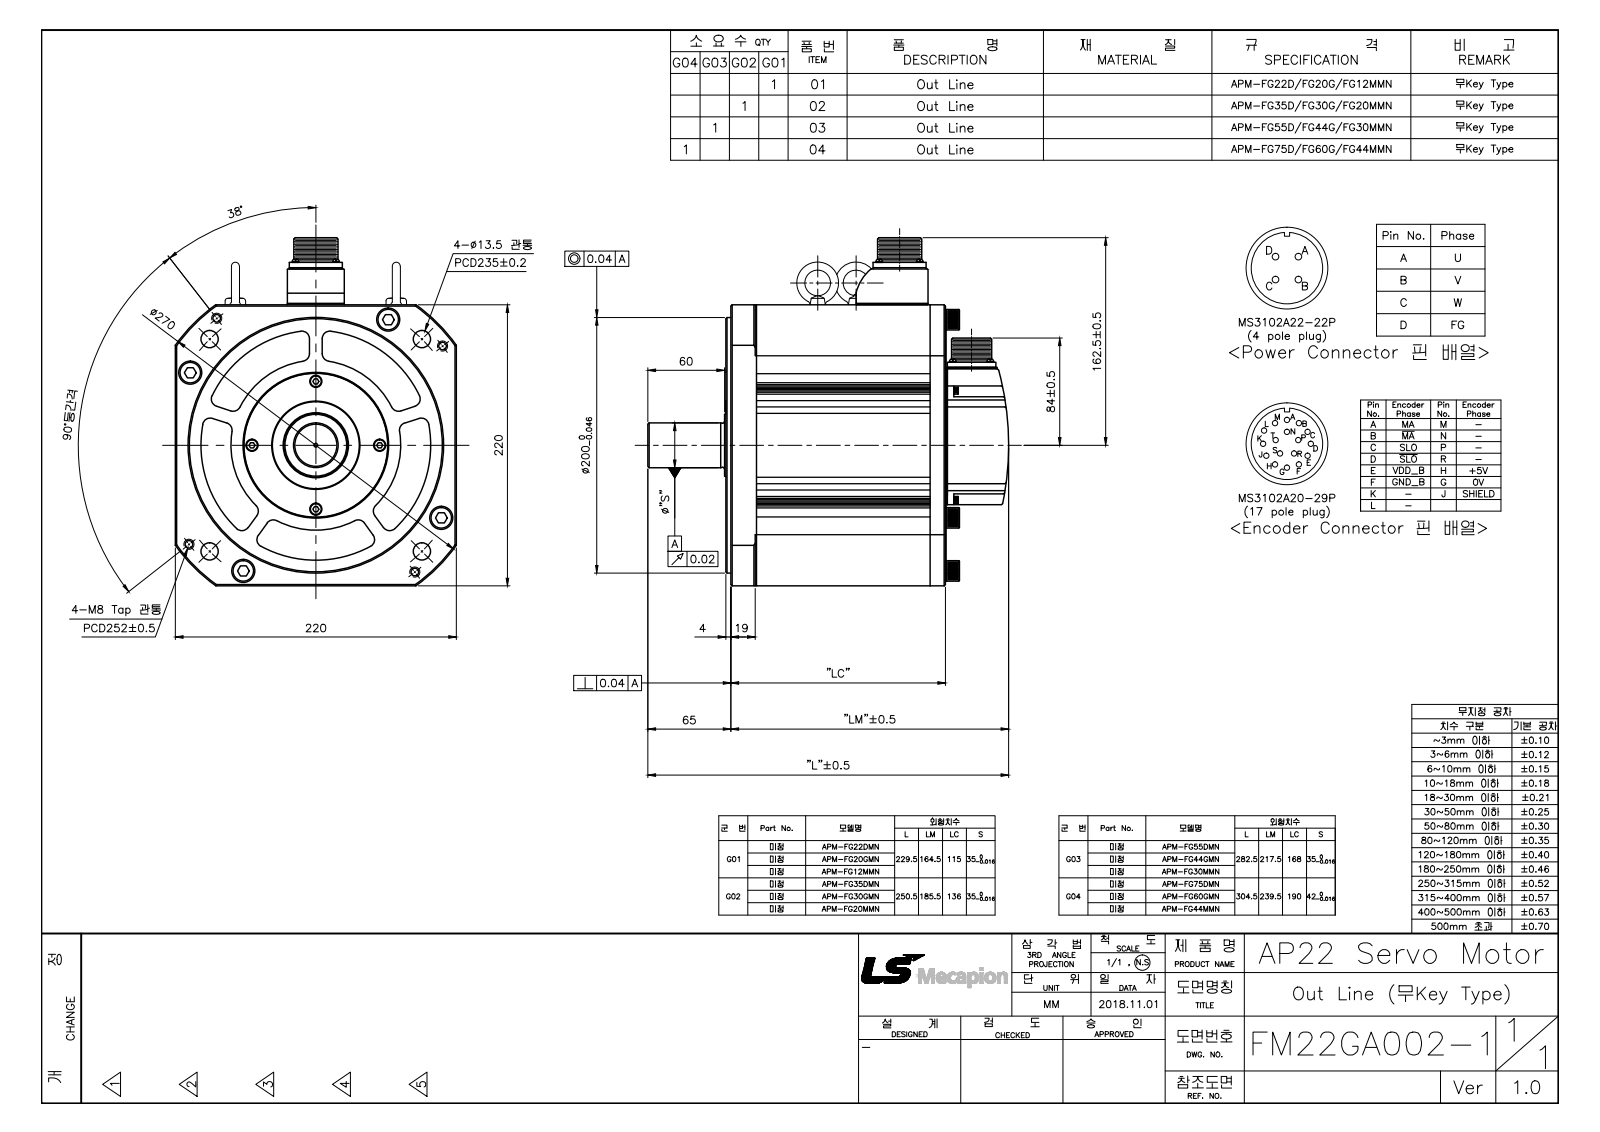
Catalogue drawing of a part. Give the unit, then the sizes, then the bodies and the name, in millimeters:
Units: millimetres
Overall size (bounding box): 282.5 × 272.5 × 220
Round holes (diameter × count): ⌀2.5 ×12, ⌀3 ×12, ⌀3.05 ×8, ⌀6 ×8, ⌀8 ×6, ⌀3.5 ×4, ⌀3.6 ×4, ⌀3.7 ×4, ⌀4.2 ×4, ⌀5 ×4, ⌀8.5 ×4, ⌀9.5 ×4
Round bosses / shafts (diameter × count): ⌀1.6 ×17, ⌀5.4 ×8, ⌀16 ×4, ⌀8.5 ×4, ⌀5.5 ×4, ⌀3 ×4, ⌀201 ×1, ⌀200 ×1
Partial cylindrical surfaces — rounded edges, fillets, slot ends (radius × count): R1 ×112, R6 ×20, R4 ×18, R2 ×17, R5 ×16, R0.5 ×12, R4.5 ×12, R0.3 ×2
Main face-to-face distances: 136, 12, 1, 148, 40, 9, 220, 180, 0.5, 13.5
Hole centre spacings: 32.56, 89.44, 156.9, 1.06, 17.11, 20.79, 22.49, 23.55
Volume: 7 583 000 mm³ · Surface area: 626 165 mm²
Bodies: 56 solids, 2105 faces (709 planar, 832 cylindrical, 564 other)
Part name (STEP PRODUCT): FM22GA002-1G03_Out Line(APM-FG55D_N,FG44G_N,FG30M_N)
STEP written by: SolidWorks 2011 (AUTOMOTIVE_DESIGN)
